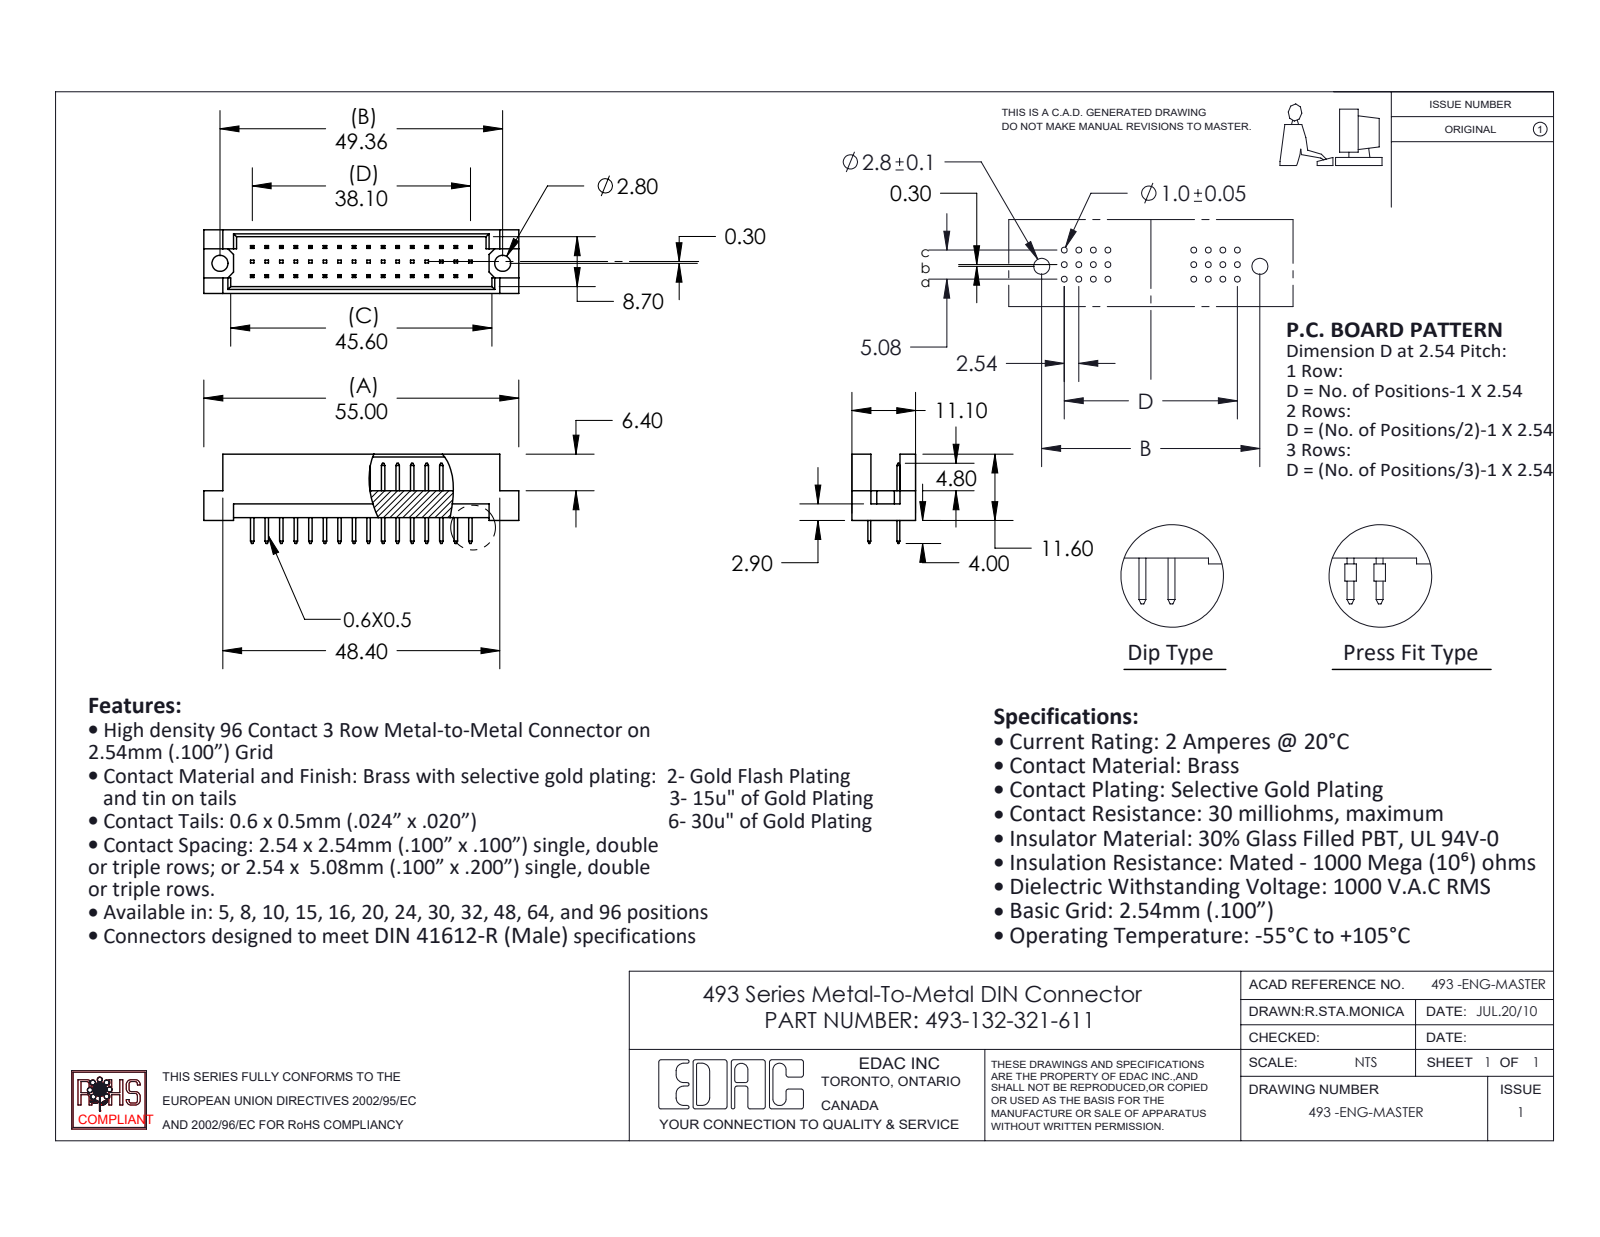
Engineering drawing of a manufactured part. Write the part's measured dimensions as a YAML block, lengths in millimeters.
part_name: "493 Part_48; 493-290_21; 493-132-321-611"
step_written_by: "SolidWorks 2020 (CONFIG_CONTROL_DESIGN)"
units: millimeters
bodies: {solids: 33, faces: 692, planar: 688, cylindrical: 4, other: 0}
overall_size: [55, 15.6, 11.1]
volume: 3403
surface_area: 4729
round_holes:
  - {diameter: 2.8, count: 2}
face_to_face_distances: [1.2, 9.9, 5.08, 11.1, 0.5, 2.54, 8.7, 4.7, 2.76, 8.34]
hole_center_spacings: [49.36]
